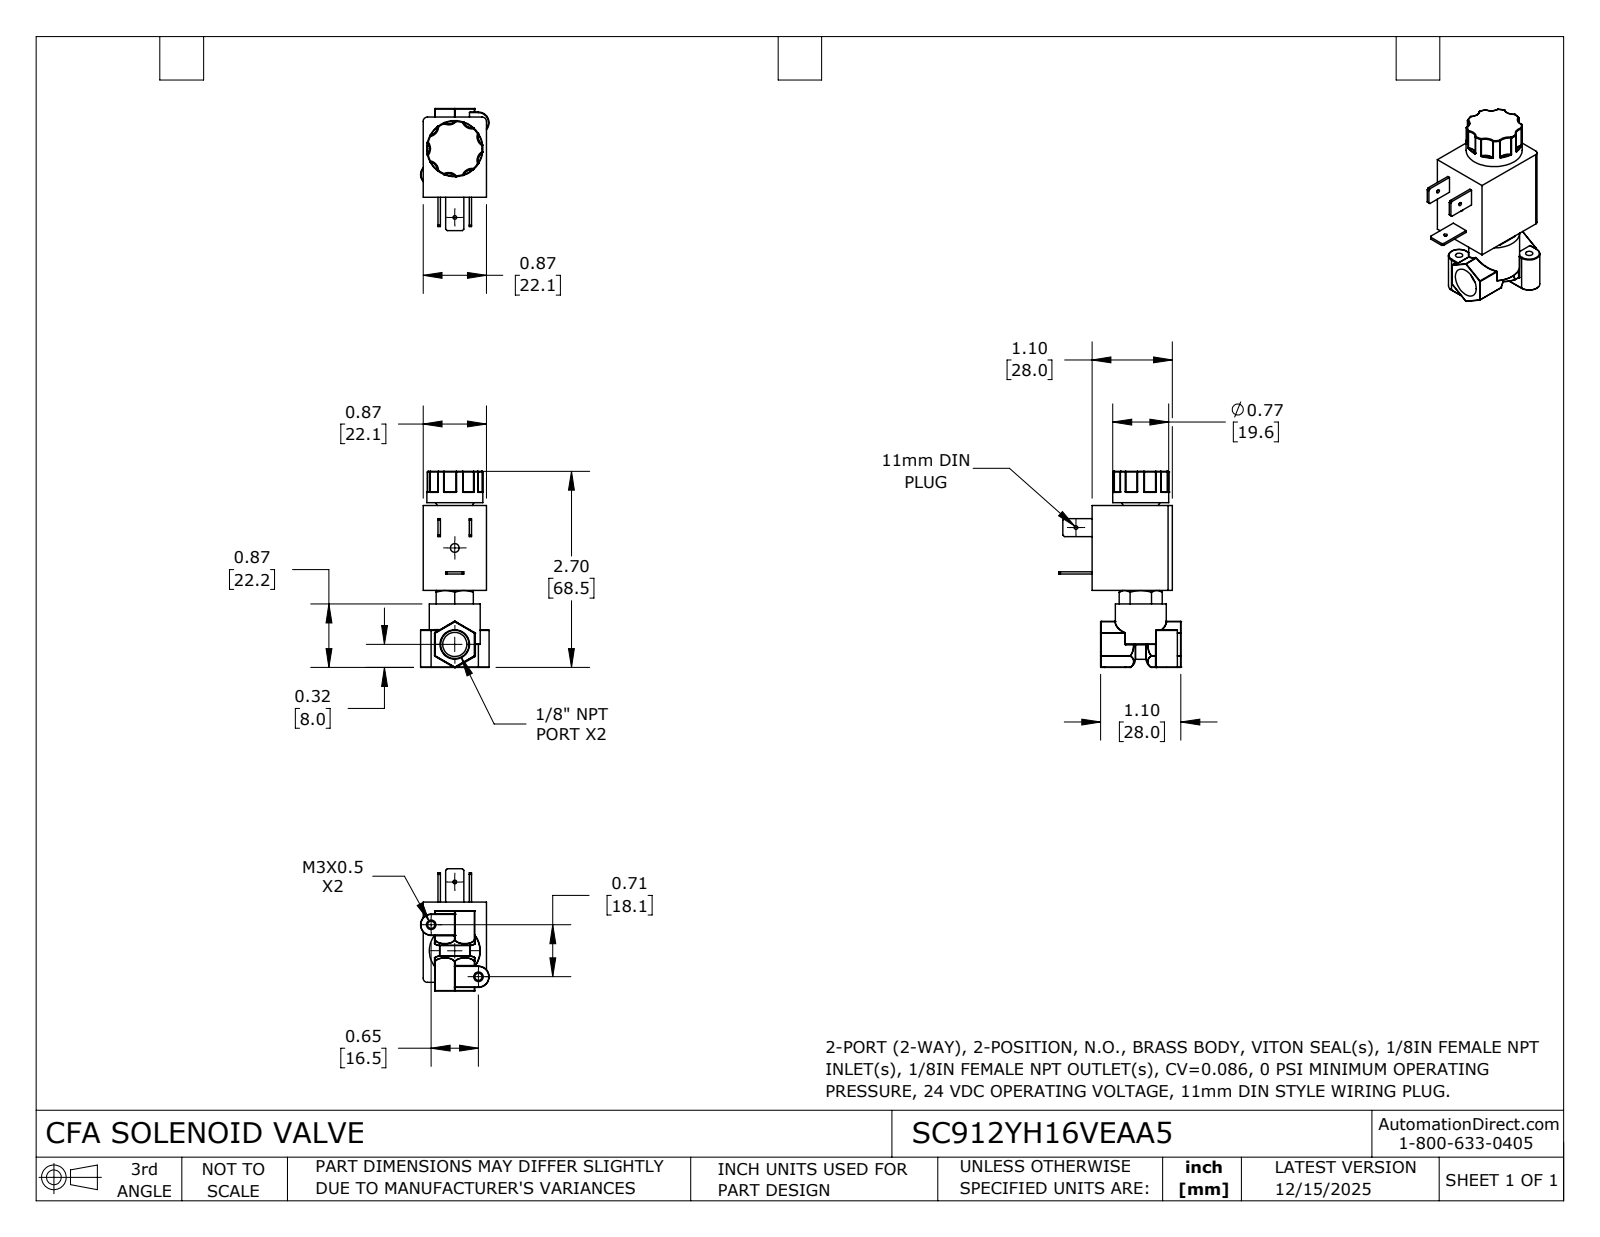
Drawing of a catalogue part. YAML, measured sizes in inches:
part_name: "SC912YH16VEAA5"
step_written_by: "SolidWorks 2024 (CONFIG_CONTROL_DESIGN)"
units: inches
bodies: {solids: 1, faces: 397, planar: 76, cylindrical: 110, other: 211}
overall_size: [2.695, 1.678, 0.942]
volume: 1.739
surface_area: 14.05
round_holes:
  - {diameter: 0.05, count: 2}
  - {diameter: 0.1, count: 2}
  - {diameter: 0.12, count: 1}
  - {diameter: 0.332, count: 1}
round_bosses_or_shafts:
  - {diameter: 0.77, count: 1}
  - {diameter: 0.7, count: 1}
partial_cylinders:
  - {radius: 0.004, count: 29}
  - {radius: 0.01, count: 18}
  - {radius: 0.008, count: 12}
  - {radius: 0.133, count: 7}
  - {radius: 0.017, count: 2}
  - {radius: 0.06, count: 2}
  - {radius: 0.132, count: 2}
  - {radius: 0.146, count: 2}
face_to_face_distances: [0.87, 1.104, 1.167, 1.637, 0.47, 0.548, 0.031, 0.161, 0.709, 1.207]
hole_center_spacings: [0.672, 0.965, 1.326, 1.342]
